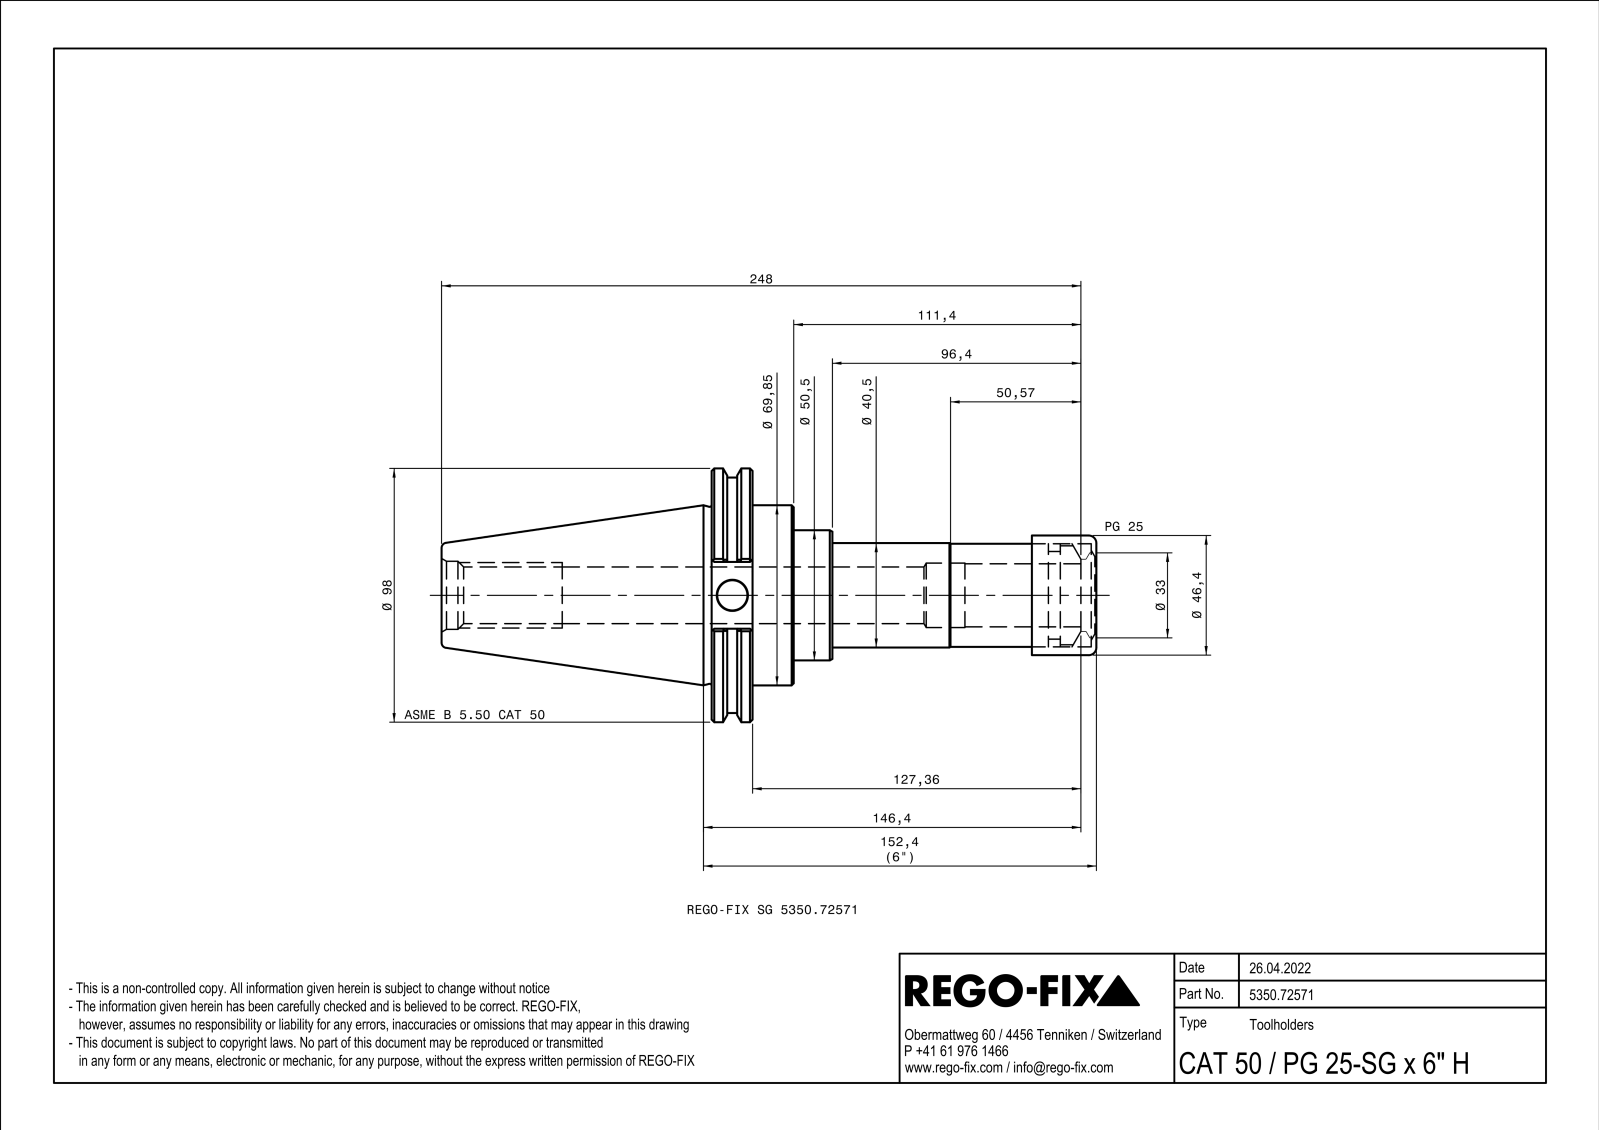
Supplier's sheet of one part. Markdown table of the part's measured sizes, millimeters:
| quantity | value |
| --- | --- |
| part name | NOCUT |
| STEP written by | SIEMENS PLM Software Solid Edge ST10 (AUTOMOTIVE_DESIGN) |
| units | millimeters |
| bodies | 1 solid, 124 faces (38 planar, 33 cylindrical, 53 other) |
| overall size | 254 × 98.42 × 94.39 |
| volume | 482 806 mm³ |
| surface area | 78 139 mm² |
| round holes (diameter × count) | 11.7 × 1, 21.96 × 1, 25 × 1, 26.4 × 1, 30 × 1, 40.05 × 1, 42 × 1 |
| round bosses / shafts (diameter × count) | 98.42 × 1, 91.3 × 1, 69.85 × 1, 50.5 × 1, 46.4 × 1, 46 × 1, 40.5 × 1, 40 × 1 |
| partial cylindrical surfaces (radius × count) | 0.5 × 12 |
| main face-to-face distances | 15.87, 15.96, 31.83, 117.4, 133.36, 149.23, 254, 136.6, 120.64, 104.77 |
